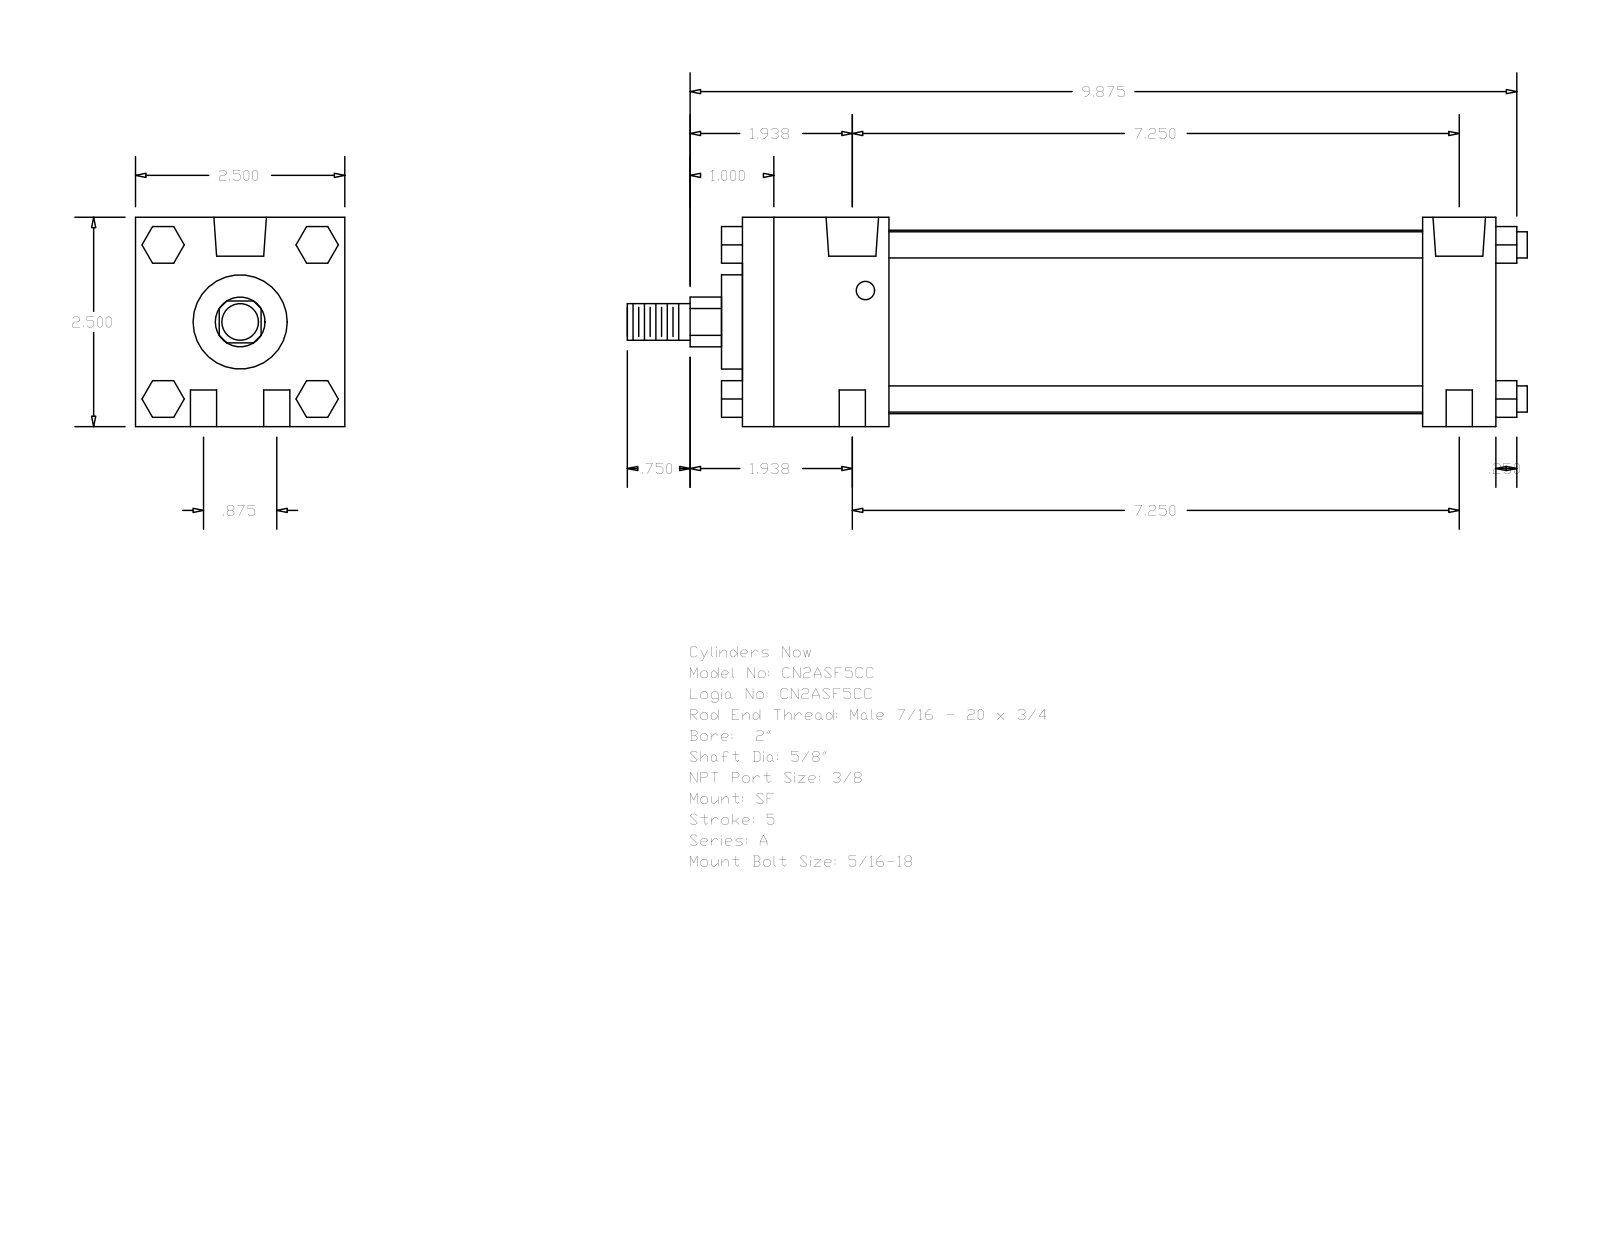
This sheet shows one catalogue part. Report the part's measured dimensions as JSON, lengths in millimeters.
{"part_name": "A_SF__0200_0.625", "step_written_by": "GSSL Pune (CONFIG_CONTROL_DESIGN)", "units": "millimeters", "bodies": {"solids": 0, "faces": 124, "planar": 94, "cylindrical": 30, "other": 0}, "overall_size": [273.05, 63.5, 63.5], "round_holes": [[7.94, 4], [5.56, 2], [15.93, 2]], "round_bosses_or_shafts": [[7.94, 4], [55.63, 1], [28.57, 1], [15.88, 1], [11.11, 1]], "partial_cylinders_radius": [[7.54, 1]], "face_to_face_distances": [63.5, 228.59, 206.37, 22.22, 44.45, 161.92, 184.14, 6.35, 234.94, 50.8], "hole_center_spacings": [11.11, 184.48, 184.15, 22.22, 185.49, 176.2]}
